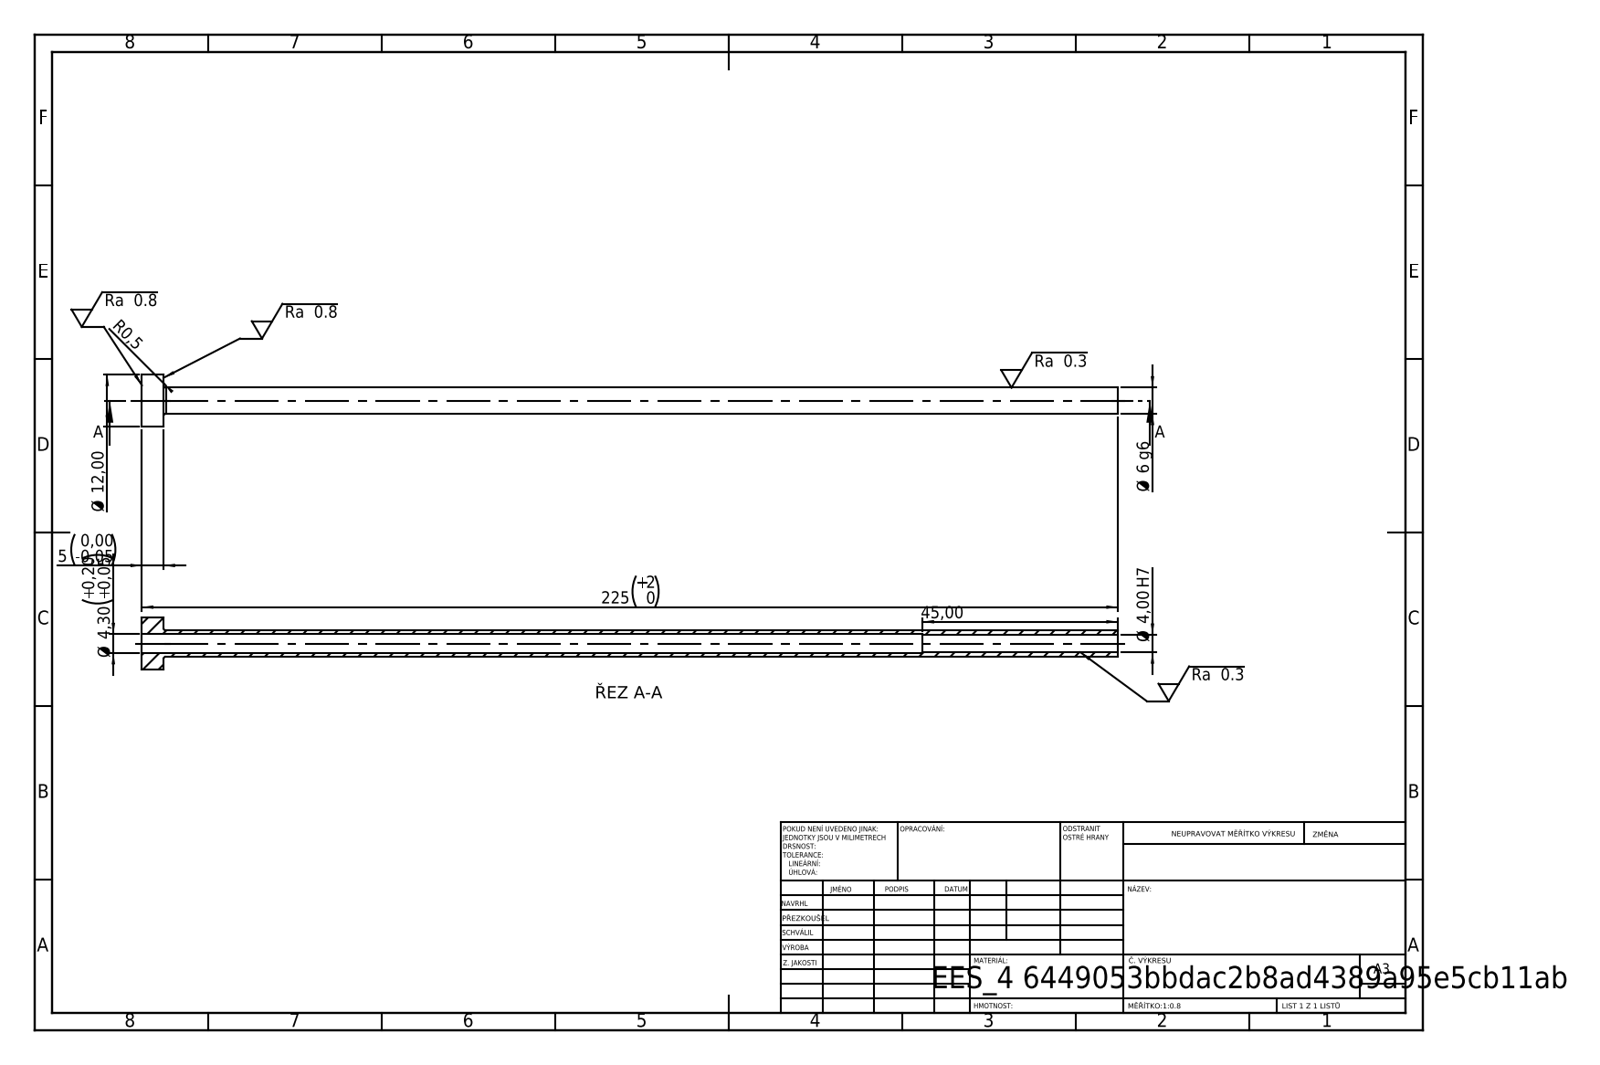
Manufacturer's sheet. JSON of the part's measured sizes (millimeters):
{"step_written_by": "SolidWorks 2019 (CONFIG_CONTROL_DESIGN)", "units": "millimeters", "bodies": {"solids": 1, "faces": 14, "planar": 4, "cylindrical": 8, "other": 2}, "overall_size": [225, 12, 12], "volume_mm3": 3607, "surface_area_mm2": 7530, "round_holes": [[4, 1], [4.3, 1]], "round_bosses_or_shafts": [[12, 1], [6, 1]], "face_to_face_distances": [5, 225, 220, 180, 175, 45]}
